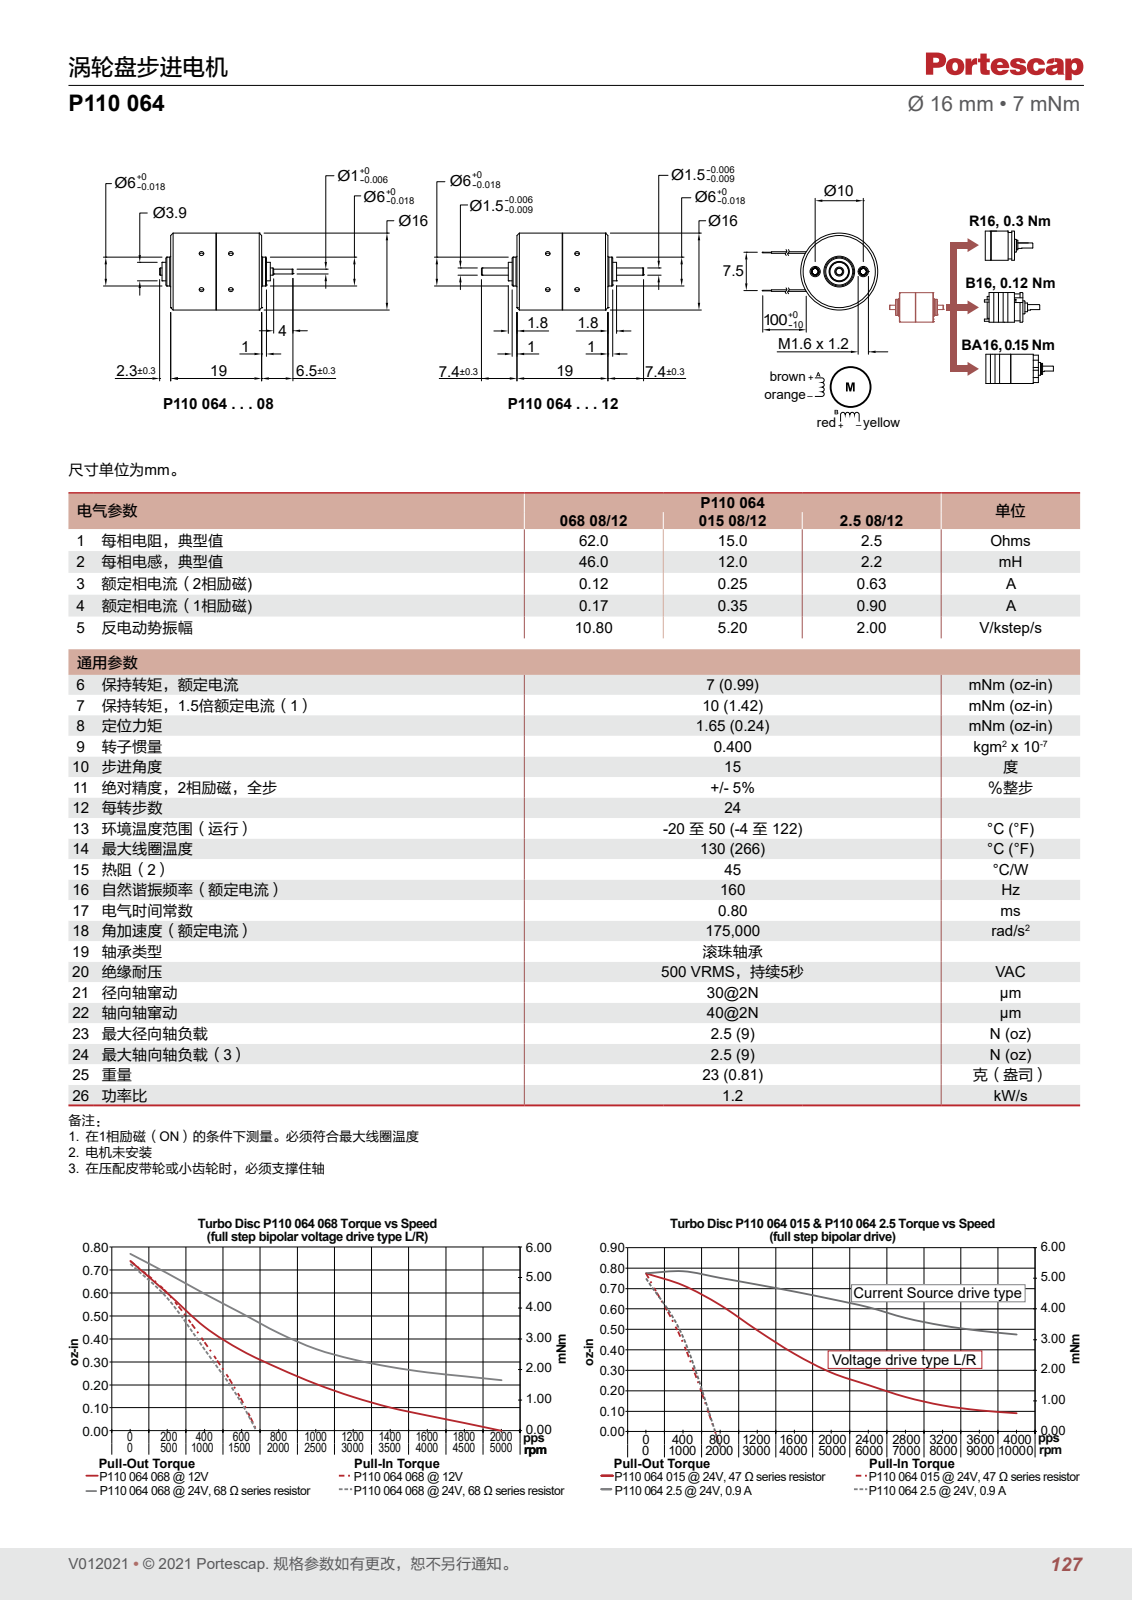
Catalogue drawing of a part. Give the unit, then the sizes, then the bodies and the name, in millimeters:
Units: millimetres
Overall size (bounding box): 29 × 24.06 × 17.34
Round holes (diameter × count): ⌀1.74 ×2, ⌀1.5 ×1, ⌀1.53 ×1, ⌀4 ×1
Round bosses / shafts (diameter × count): ⌀0.95 ×4, ⌀0.5 ×4, ⌀16 ×1, ⌀15.64 ×1, ⌀6 ×1, ⌀5.44 ×1, ⌀5.18 ×1, ⌀3.9 ×1
Partial cylindrical surfaces — rounded edges, fillets, slot ends (radius × count): R1 ×4, R7.65 ×1, R8.05 ×1
Main face-to-face distances: 9.6, 9.4, 8.58, 8.78, 16.38, 7.8, 7.6, 0.82, 17.2, 19
Hole centre spacings: 5, 10
Volume: 7 173 mm³ · Surface area: 4 194 mm²
Bodies: 18 solids, 218 faces (42 planar, 92 cylindrical, 84 other)
Part name (STEP PRODUCT): 2-800-10-0018_3; 2-420-10-0001_ASM_3_ASM; 2-800-10-0022_4; 2-280-10-0016_ASM_1_ASM (+8 more)
STEP written by: PRO/ENGINEER BY PARAMETRIC TECHNOLOGY CORPORATION, 2014310 (CONFIG_CONTROL_DESIGN)
